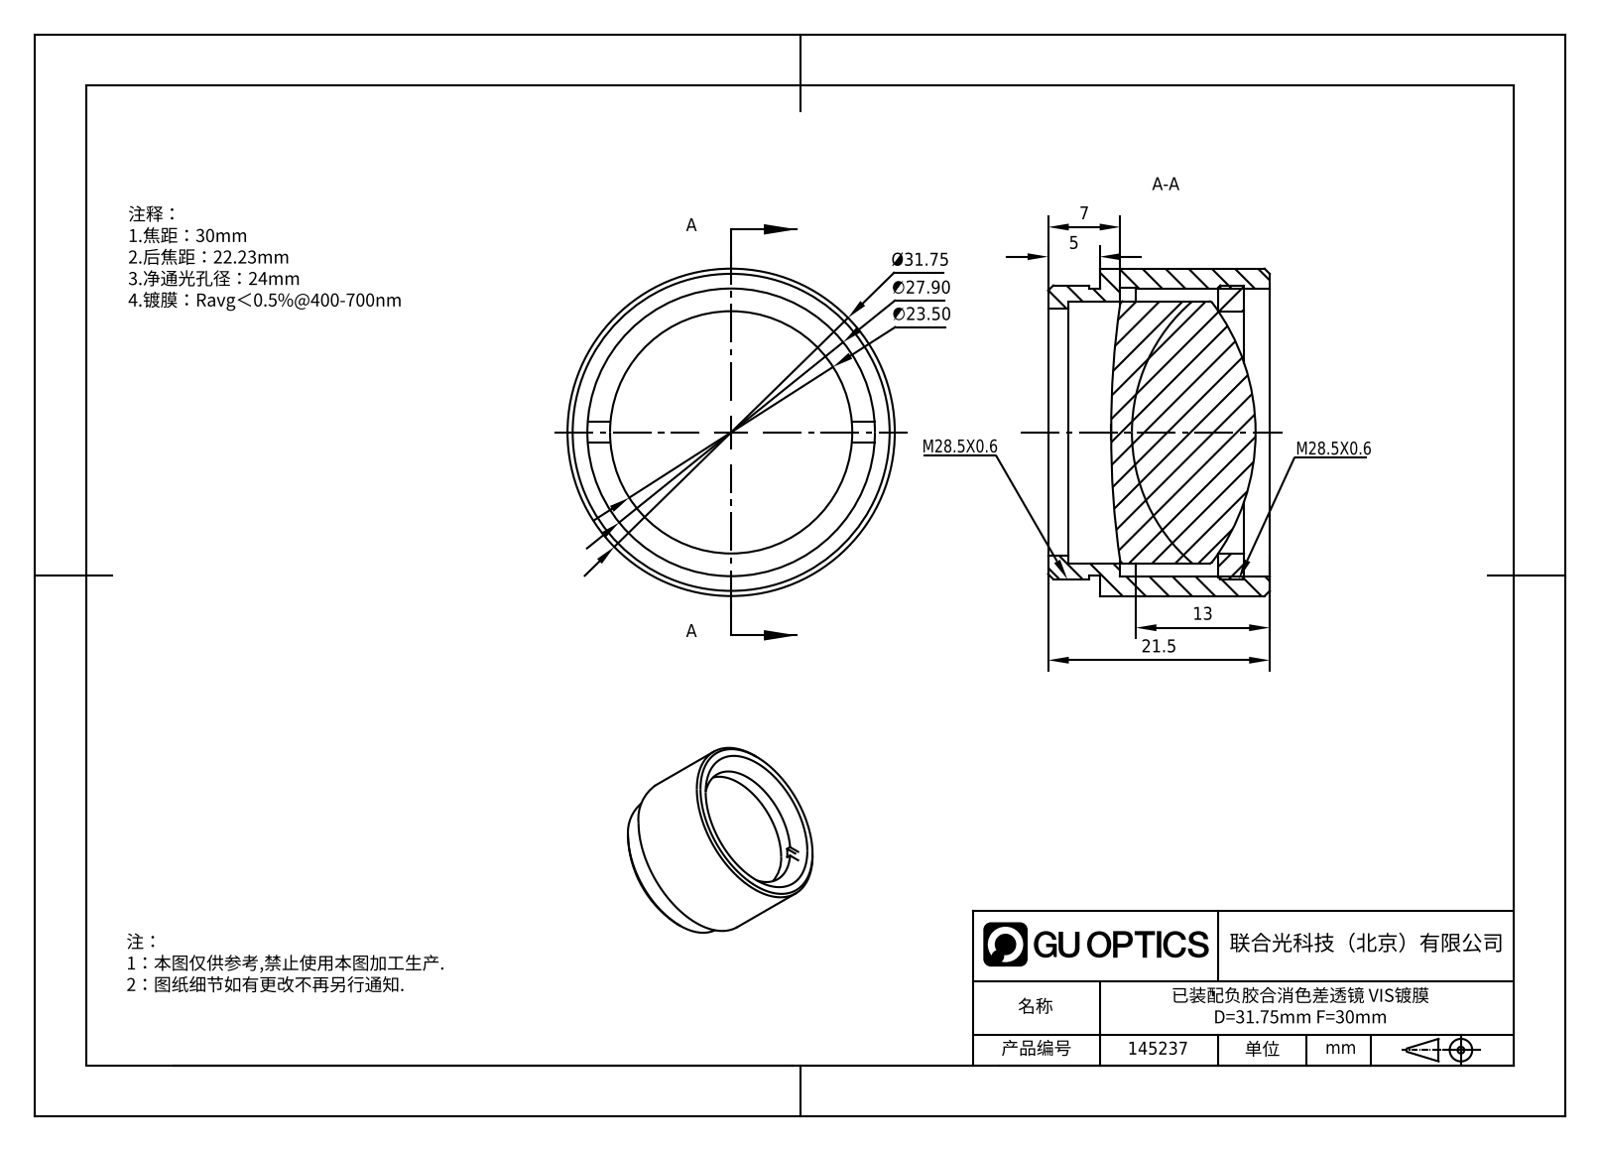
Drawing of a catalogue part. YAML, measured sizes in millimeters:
part_name: "APD-ML25-030-VIS; M28.5x0.6安装环PN35021-LM254-D2; GL31-025B-030-VIS_Solidworks; M28.5x0.6ѹȦ"
step_written_by: "SolidWorks 2022 (AUTOMOTIVE_DESIGN)"
units: millimeters
bodies: {solids: 4, faces: 56, planar: 16, cylindrical: 22, other: 18}
overall_size: [31.76, 31.76, 21.5]
volume: 10222
surface_area: 8412
round_holes:
  - {diameter: 23.5, count: 1}
  - {diameter: 24, count: 1}
  - {diameter: 27.9, count: 1}
  - {diameter: 28, count: 1}
round_bosses_or_shafts:
  - {diameter: 31.76, count: 1}
  - {diameter: 28.5, count: 1}
  - {diameter: 27.8, count: 1}
  - {diameter: 25.4, count: 1}
face_to_face_distances: [2, 5, 2.5, 11.51, 14.01, 16.51, 19.01, 21.5, 16.5, 4.99]
